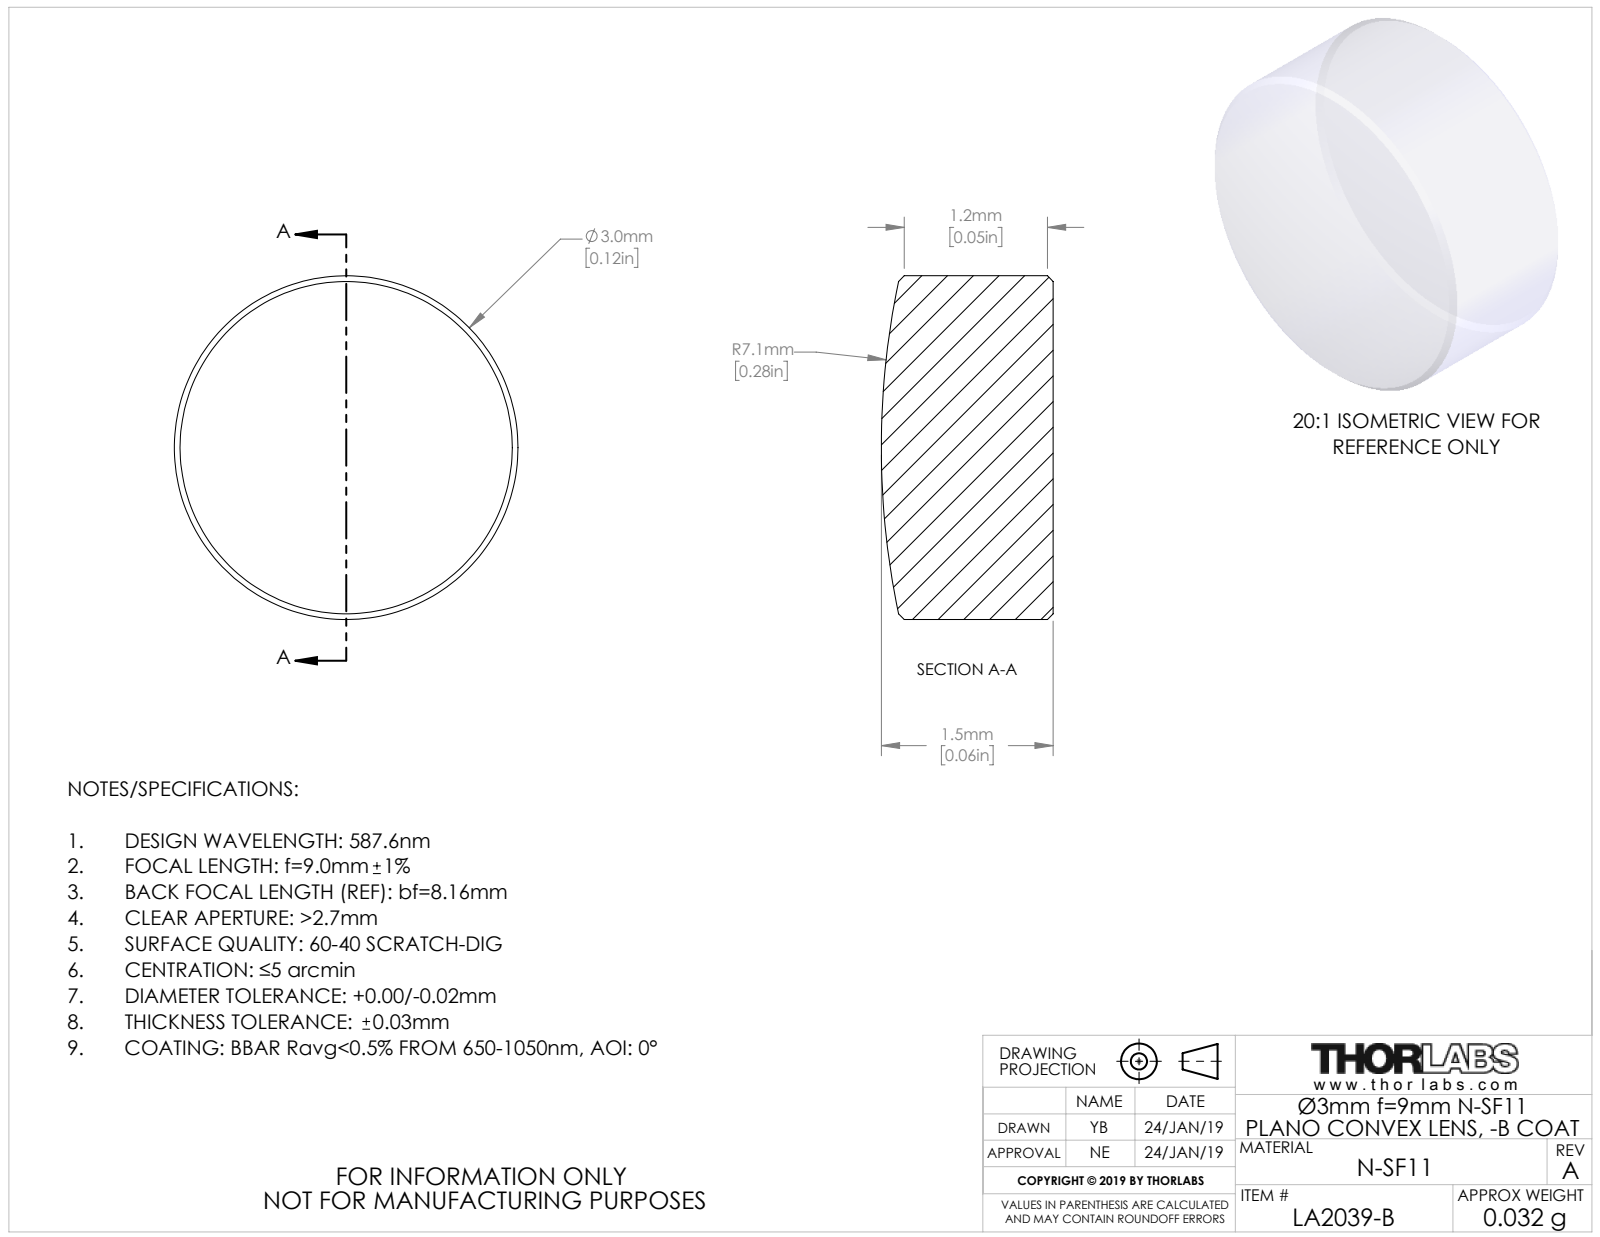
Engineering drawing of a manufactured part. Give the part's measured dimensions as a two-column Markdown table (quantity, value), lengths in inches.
| quantity | value |
| --- | --- |
| part name | TTN162756-E0W |
| STEP written by | SolidWorks 2018 (CONFIG_CONTROL_DESIGN) |
| units | inches |
| bodies | 1 solid, 9 faces (1 planar, 2 cylindrical, 6 other) |
| overall size | 0.118 × 0.118 × 0.059 |
| volume | 0.001 in³ |
| surface area | 0.04 in² |
| round bosses / shafts (diameter × count) | 0.118 × 1 |
